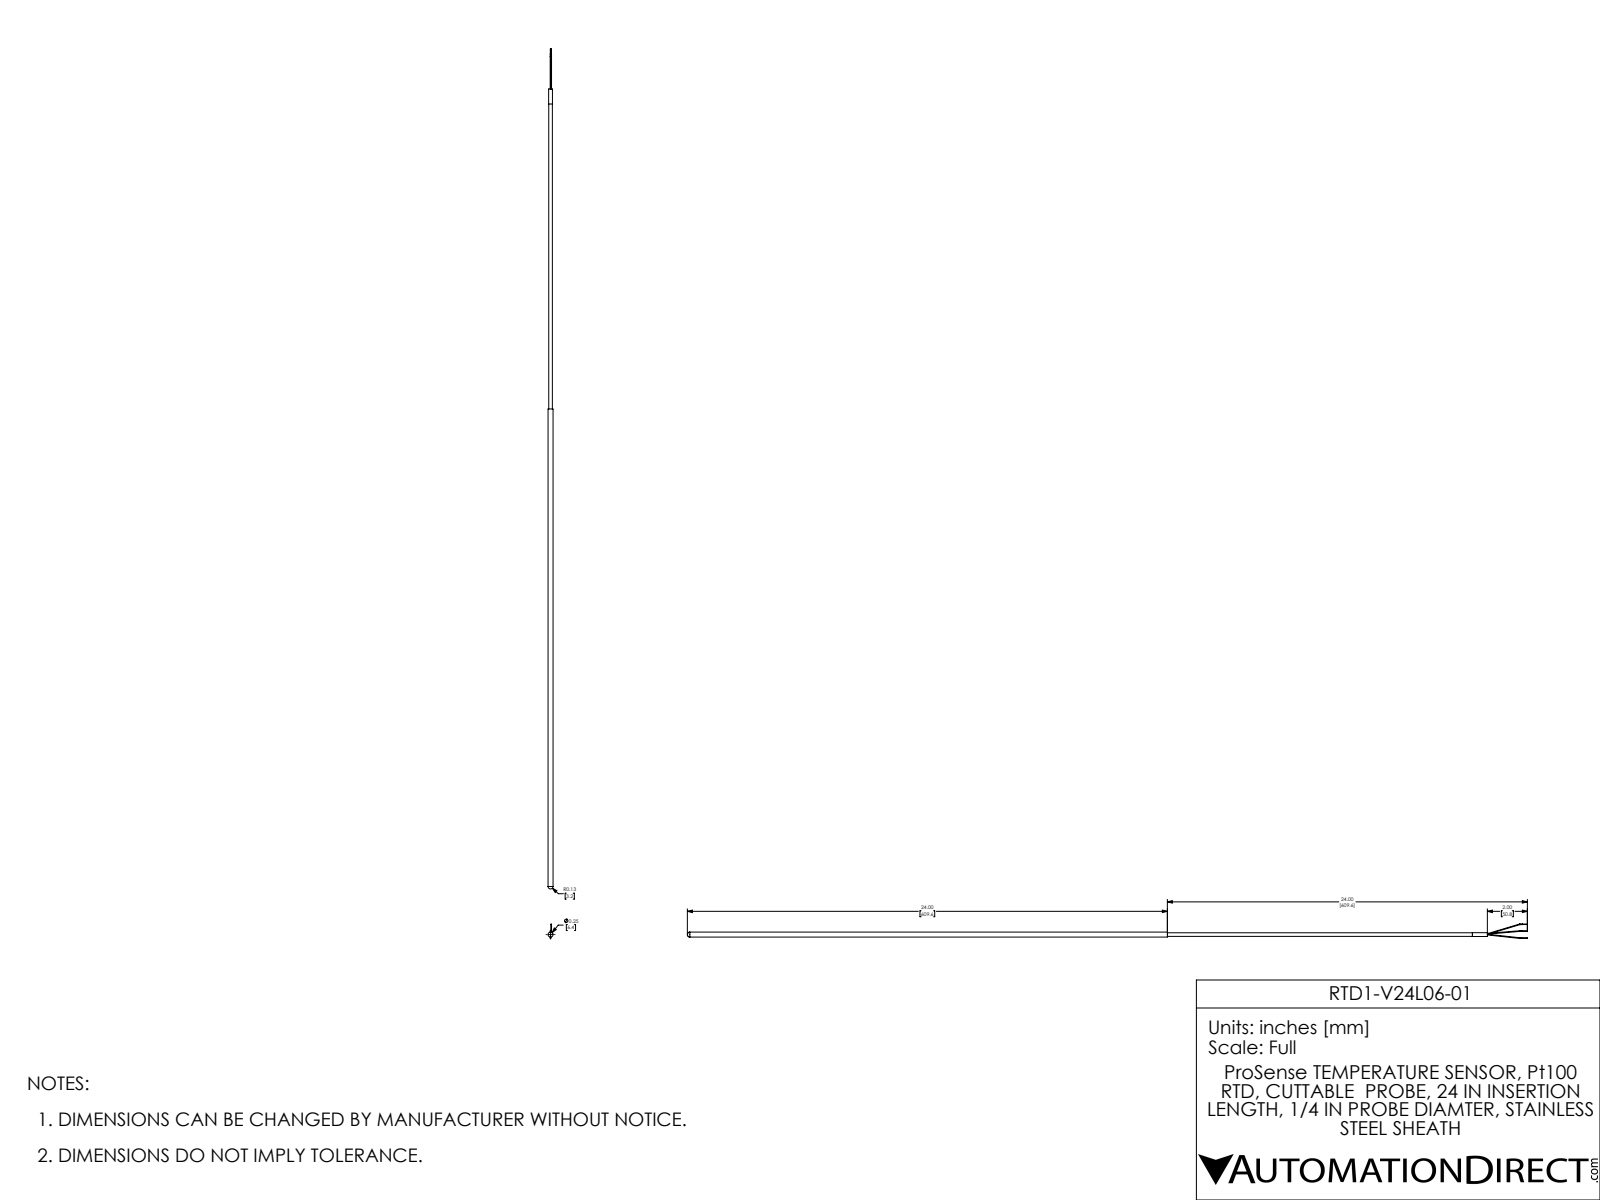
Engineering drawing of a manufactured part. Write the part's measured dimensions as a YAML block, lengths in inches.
part_name: "RTD1-V24L06-01"
step_written_by: "SolidWorks 2017 (AUTOMOTIVE_DESIGN)"
units: inches
bodies: {solids: 4, faces: 44, planar: 13, cylindrical: 24, other: 7}
overall_size: [41.995, 0.725, 0.25]
volume: 1.597
surface_area: 29.33
round_bosses_or_shafts:
  - {diameter: 0.035, count: 5}
  - {diameter: 0.025, count: 3}
  - {diameter: 0.25, count: 1}
  - {diameter: 0.19, count: 1}
  - {diameter: 0.18, count: 1}
  - {diameter: 0.035, count: 1}
face_to_face_distances: [16, 2, 0.75, 15.25, 1.25, 14, 2.75, 4, 18, 0.25]
